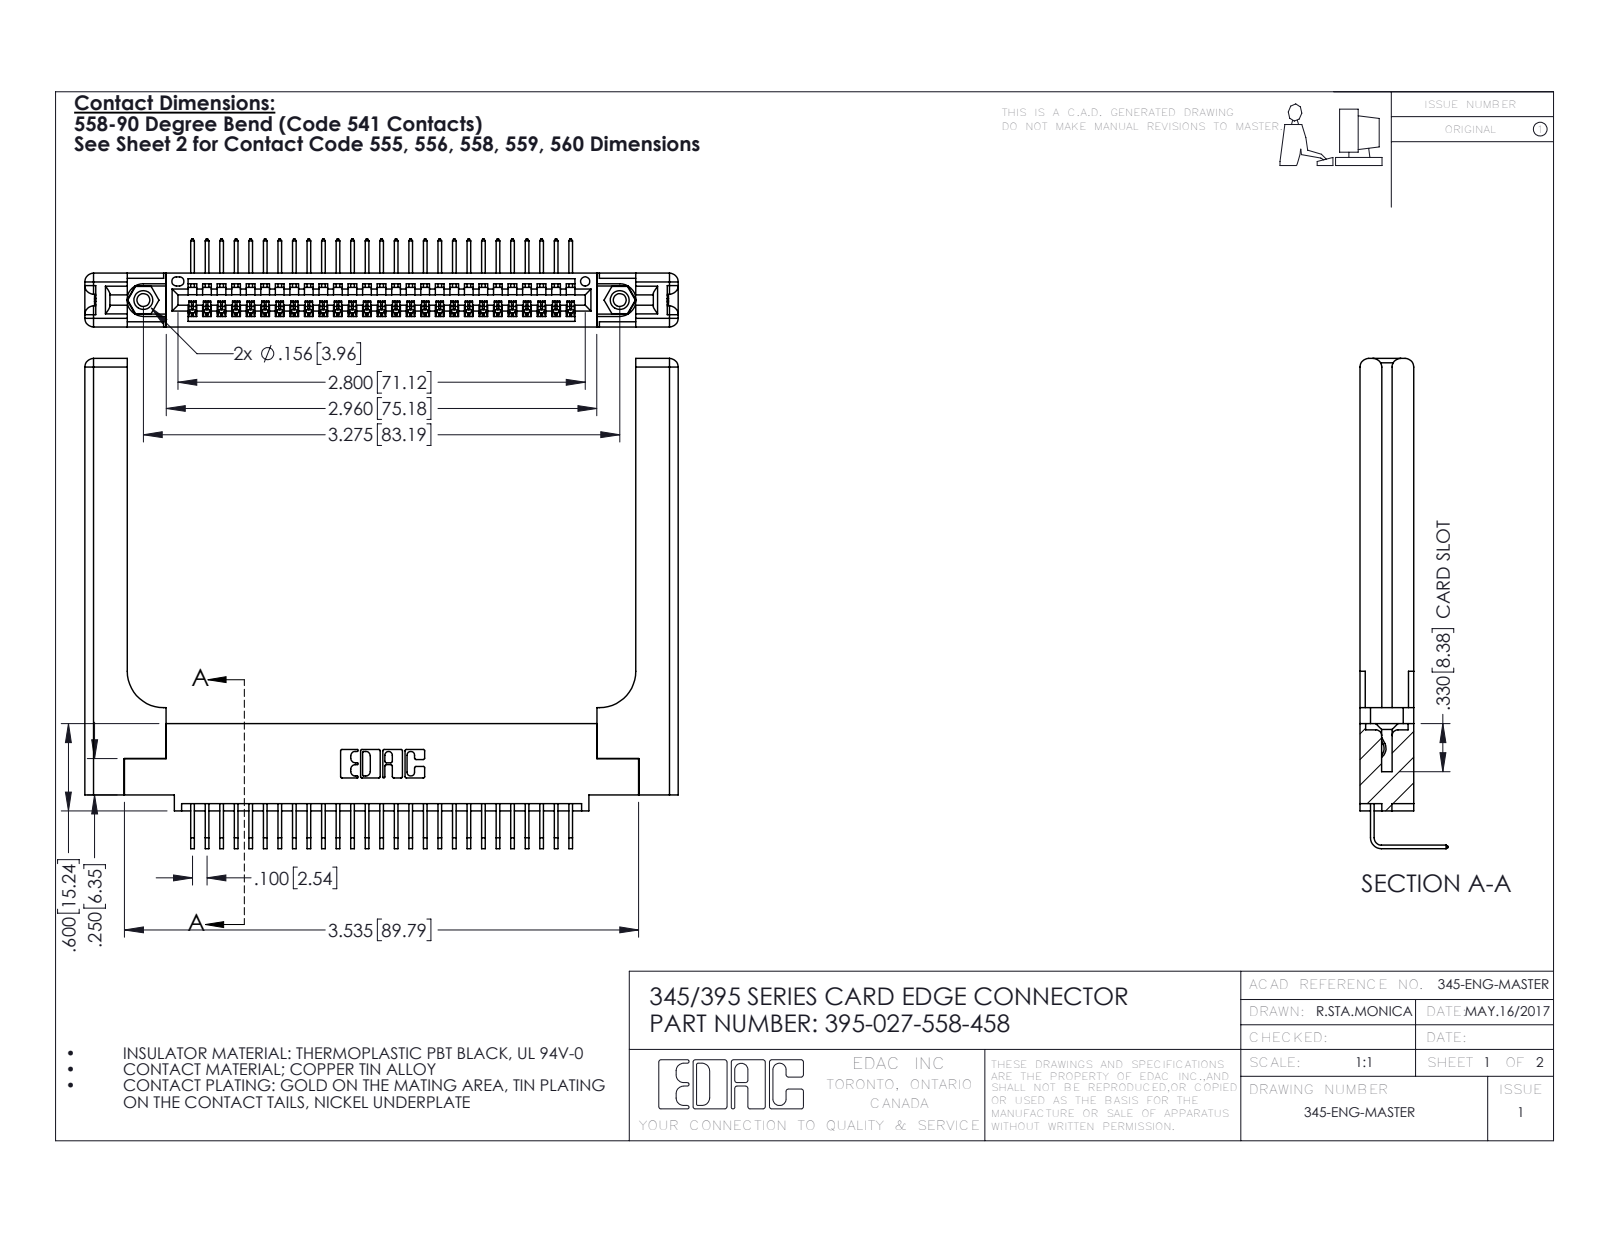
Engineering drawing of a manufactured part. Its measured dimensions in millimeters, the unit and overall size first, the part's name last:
Units: millimetres
Overall size (bounding box): 103.6 × 85.6 × 15.4
Round holes (diameter × count): ⌀2.3 ×2, ⌀3.2 ×2, ⌀4 ×2, ⌀1.6 ×1
Round bosses / shafts (diameter × count): ⌀3.9 ×2
Partial cylindrical surfaces — rounded edges, fillets, slot ends (radius × count): R0.2 ×54, R0.3 ×22, R1.5 ×16, R0.2 ×6, R0.8 ×6, R0.7 ×3, R0.8 ×2, R0.8 ×2
Main face-to-face distances: 9.4, 1.8, 7.6, 3.8, 3.8, 2.5, 6.9, 0.6, 5.1, 2
Hole centre spacings: 6.9, 77.2, 83.2
Volume: 18 240 mm³ · Surface area: 18 650 mm²
Bodies: 32 solids, 2006 faces (1366 planar, 580 cylindrical, 60 other)
Part name (STEP PRODUCT): 395-027-558-458; 345-250-001_345-250-001-102; 345-220-058_345-220-058; 345-292-001_558 Tail - 2 (+1 more)
STEP written by: SolidWorks 2016 (CONFIG_CONTROL_DESIGN)
